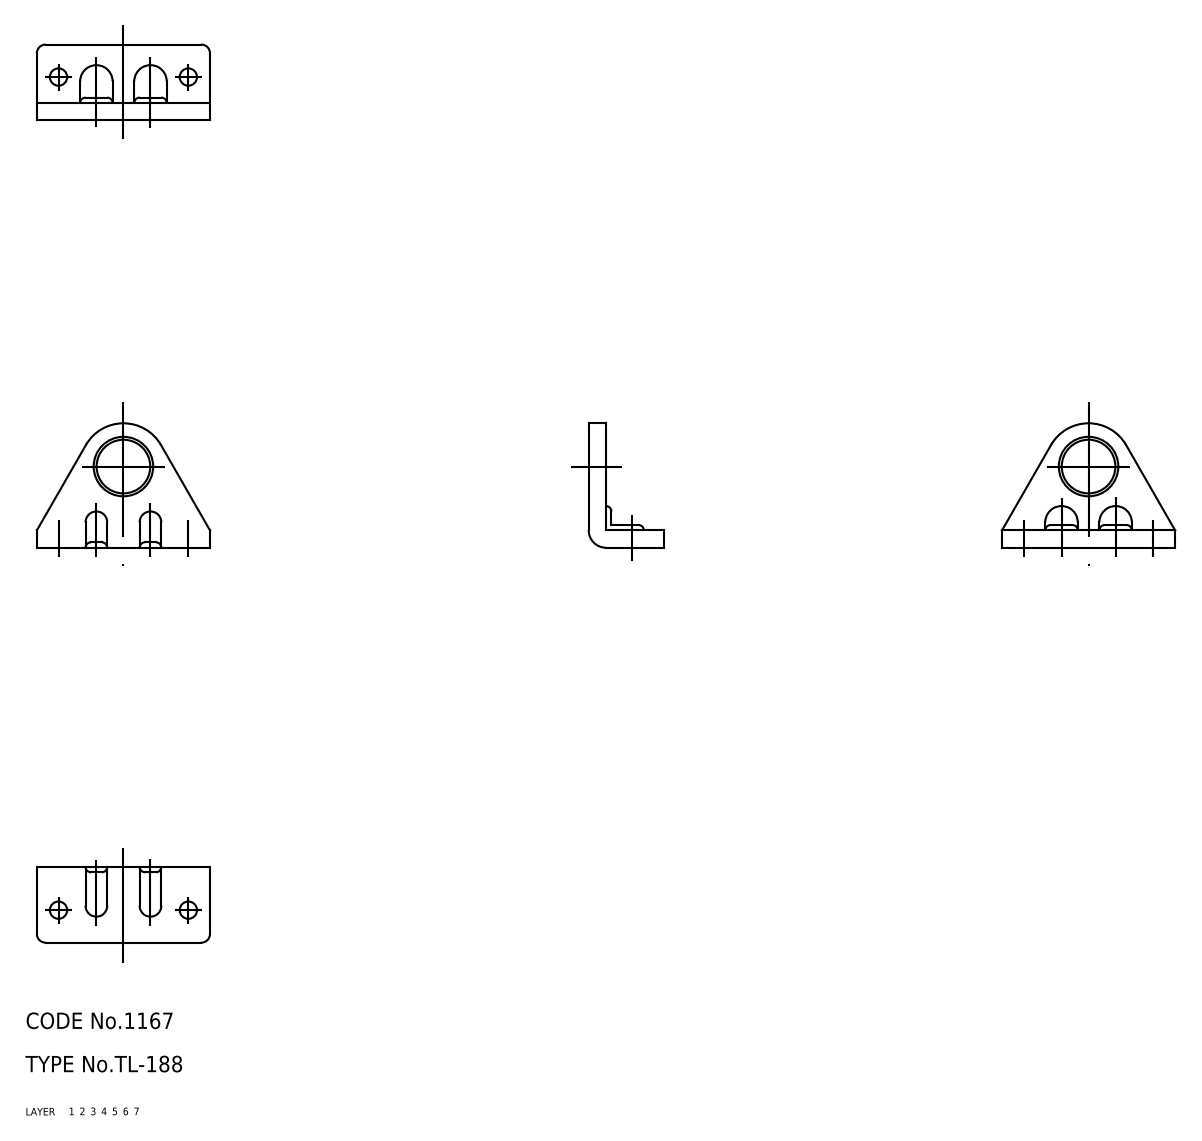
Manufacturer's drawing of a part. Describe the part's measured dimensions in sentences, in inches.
The part is named "bracket". Its 3-D file was written by "CADfix (AUTOMOTIVE_DESIGN)". It is 1 solid with 61 faces: 0 planar, 0 cylindrical and 61 other. Overall it measures 1.26 by 0.906 by 0.551 inches. Its volume is 0.14 cubic inches and its surface area 3.089 square inches.
